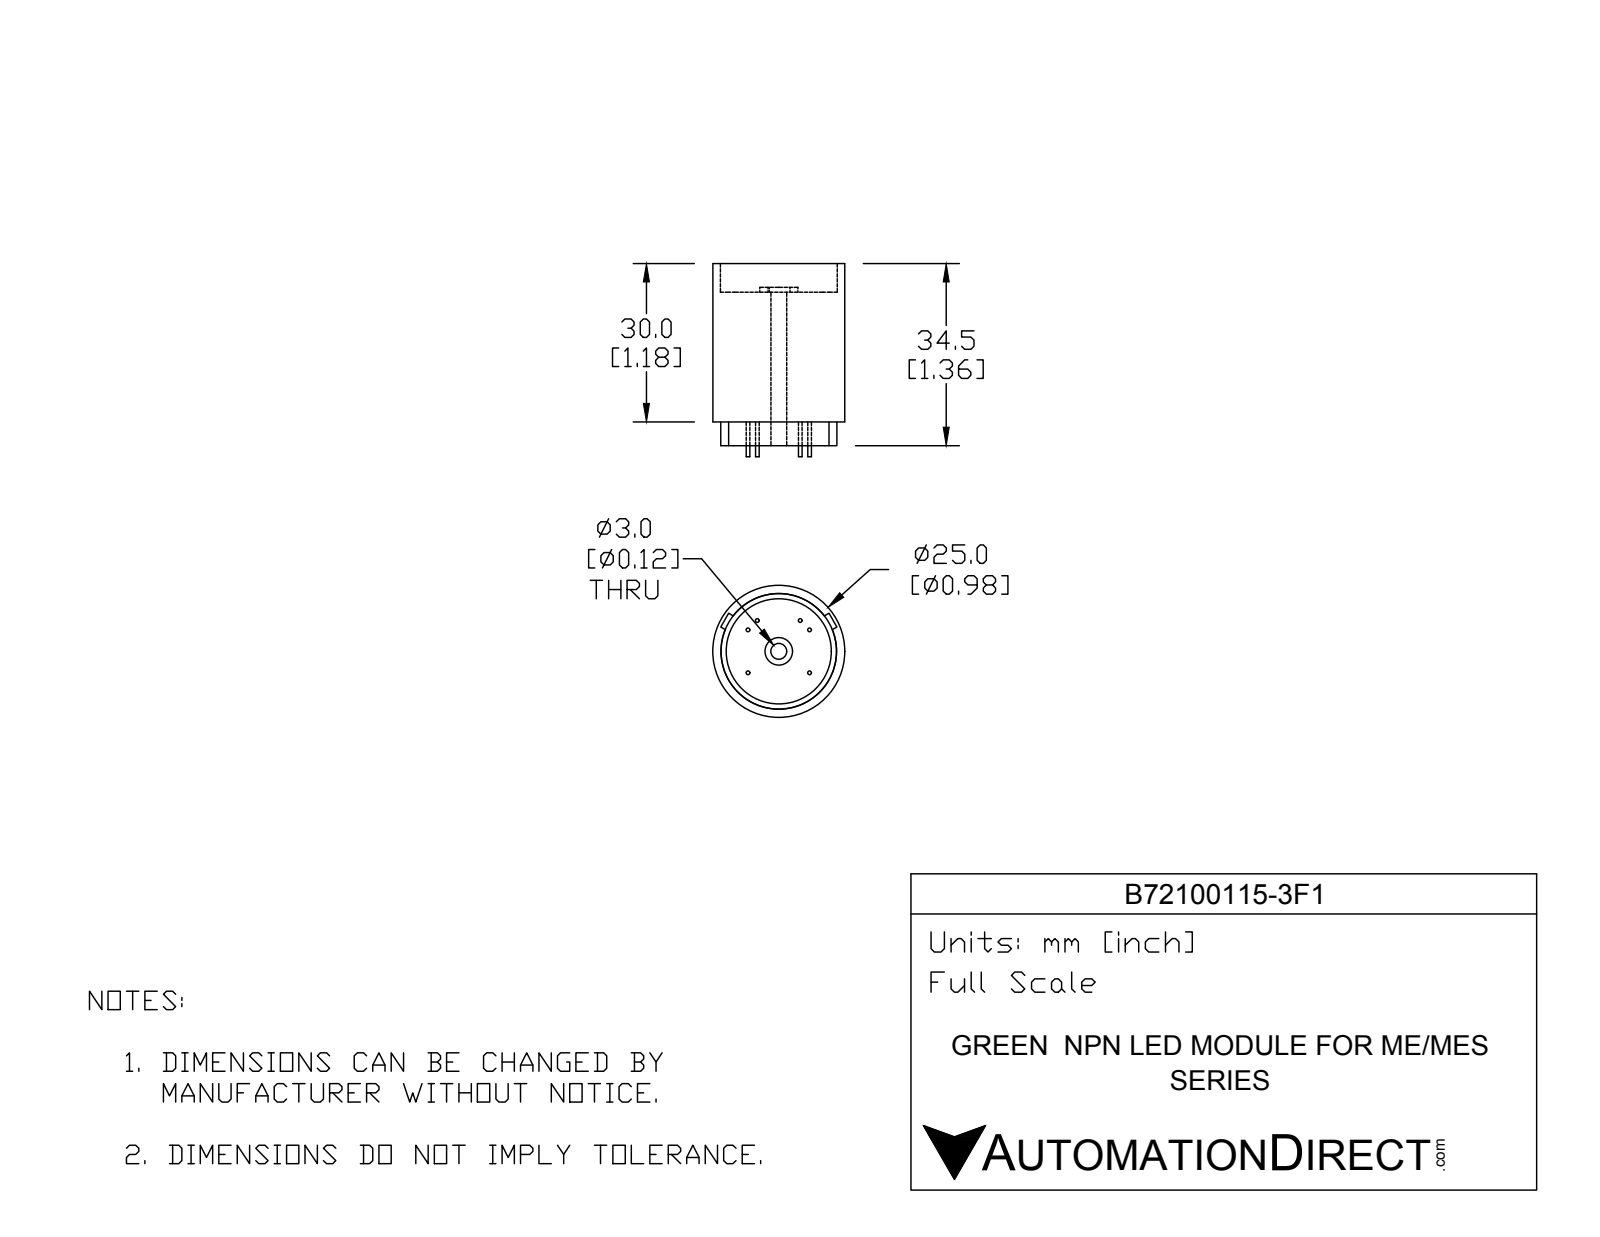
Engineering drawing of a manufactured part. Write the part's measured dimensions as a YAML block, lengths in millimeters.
part_name: "B72100115-3F1"
step_written_by: "SolidWorks 2016 (AUTOMOTIVE_DESIGN)"
units: millimeters
bodies: {solids: 9, faces: 69, planar: 36, cylindrical: 33, other: 0}
overall_size: [36.6, 25, 25]
volume: 12963
surface_area: 4884
round_holes:
  - {diameter: 3, count: 1}
  - {diameter: 4.22, count: 1}
  - {diameter: 19.9, count: 1}
  - {diameter: 21.5, count: 1}
round_bosses_or_shafts:
  - {diameter: 0.7, count: 6}
  - {diameter: 25, count: 1}
  - {diameter: 21.9, count: 1}
  - {diameter: 7.22, count: 1}
  - {diameter: 5.2, count: 1}
face_to_face_distances: [24.56, 30, 5.44, 4.5, 29.06, 34.5, 25.5, 0.94, 3.05, 3.1]
